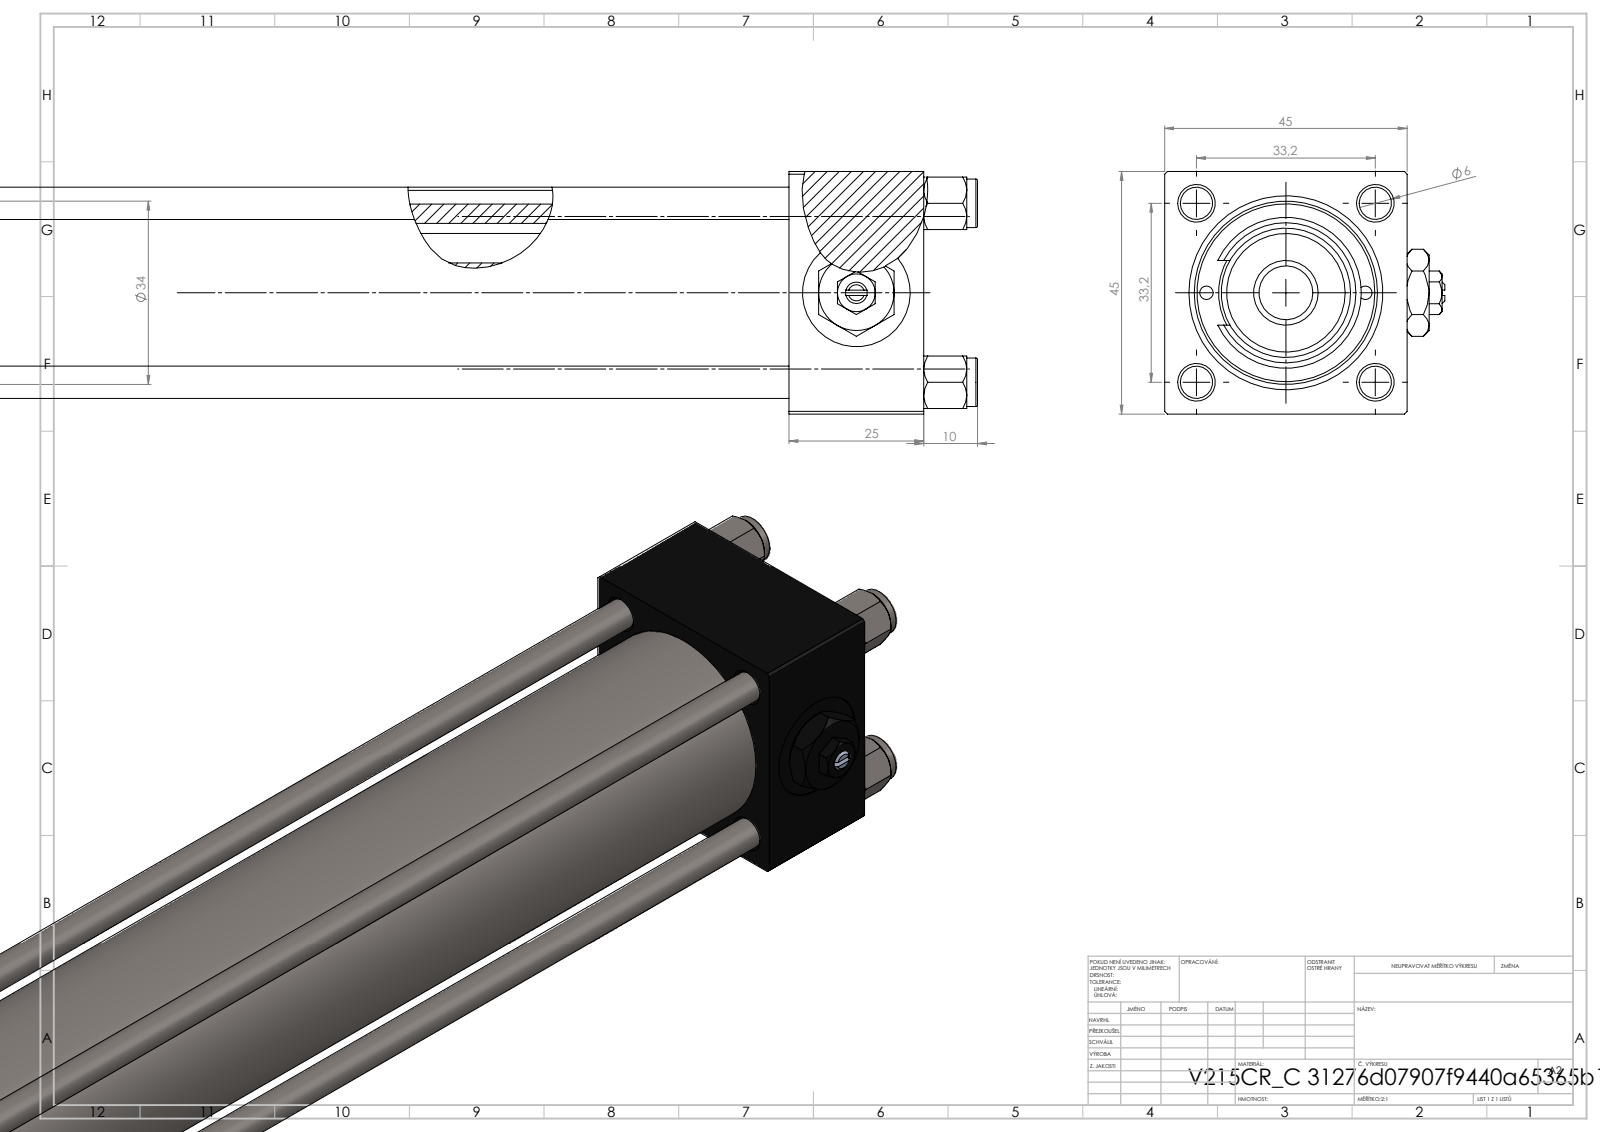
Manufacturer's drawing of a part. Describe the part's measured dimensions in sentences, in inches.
The part is named "NUT_M5_C; Zatka_pro_OIL_PORT; V215CR_C_TYCINKA; V215CR_C_Body (+4 more)". Its 3-D file was written by "SolidWorks 2019 (CONFIG_CONTROL_DESIGN)". It is 15 solids with 1339 faces: 602 planar, 115 cylindrical and 622 other. Overall it measures 17.677 by 2.047 by 1.772 inches. Its volume is 25.35 cubic inches and its surface area 254.7 square inches. Round holes: 4 of diameter 0.236, 2 of diameter 0.098, 2 of diameter 0.276, 2 of diameter 0.518, 2 of diameter 0.787, 1 of diameter 0.413, 1 of diameter 0.866, 1 of diameter 0.945, 1 of diameter 0.984, 1 of diameter 1.26, 1 of diameter 1.299. Round bosses or shafts: 4 of diameter 0.354, 1 of diameter 1.496, 1 of diameter 1.339, 1 of diameter 1.102, 1 of diameter 0.709, 1 of diameter 0.472, 1 of diameter 0.433, 1 of diameter 0.394. Partial cylindrical surfaces (rounded edges, fillets, slot ends): 1 of radius 0.384, 1 of radius 0.413. The main face-to-face distances are 1.772, 0.984, 13.898, 12.008, 11.024, 12.913, 1.764, 0.512, 1.89, 12.768. The hole center spacings are 0.657, 0.924, 1.307, 1.396, 0.581, 1.848, 1.161, 12.028.
